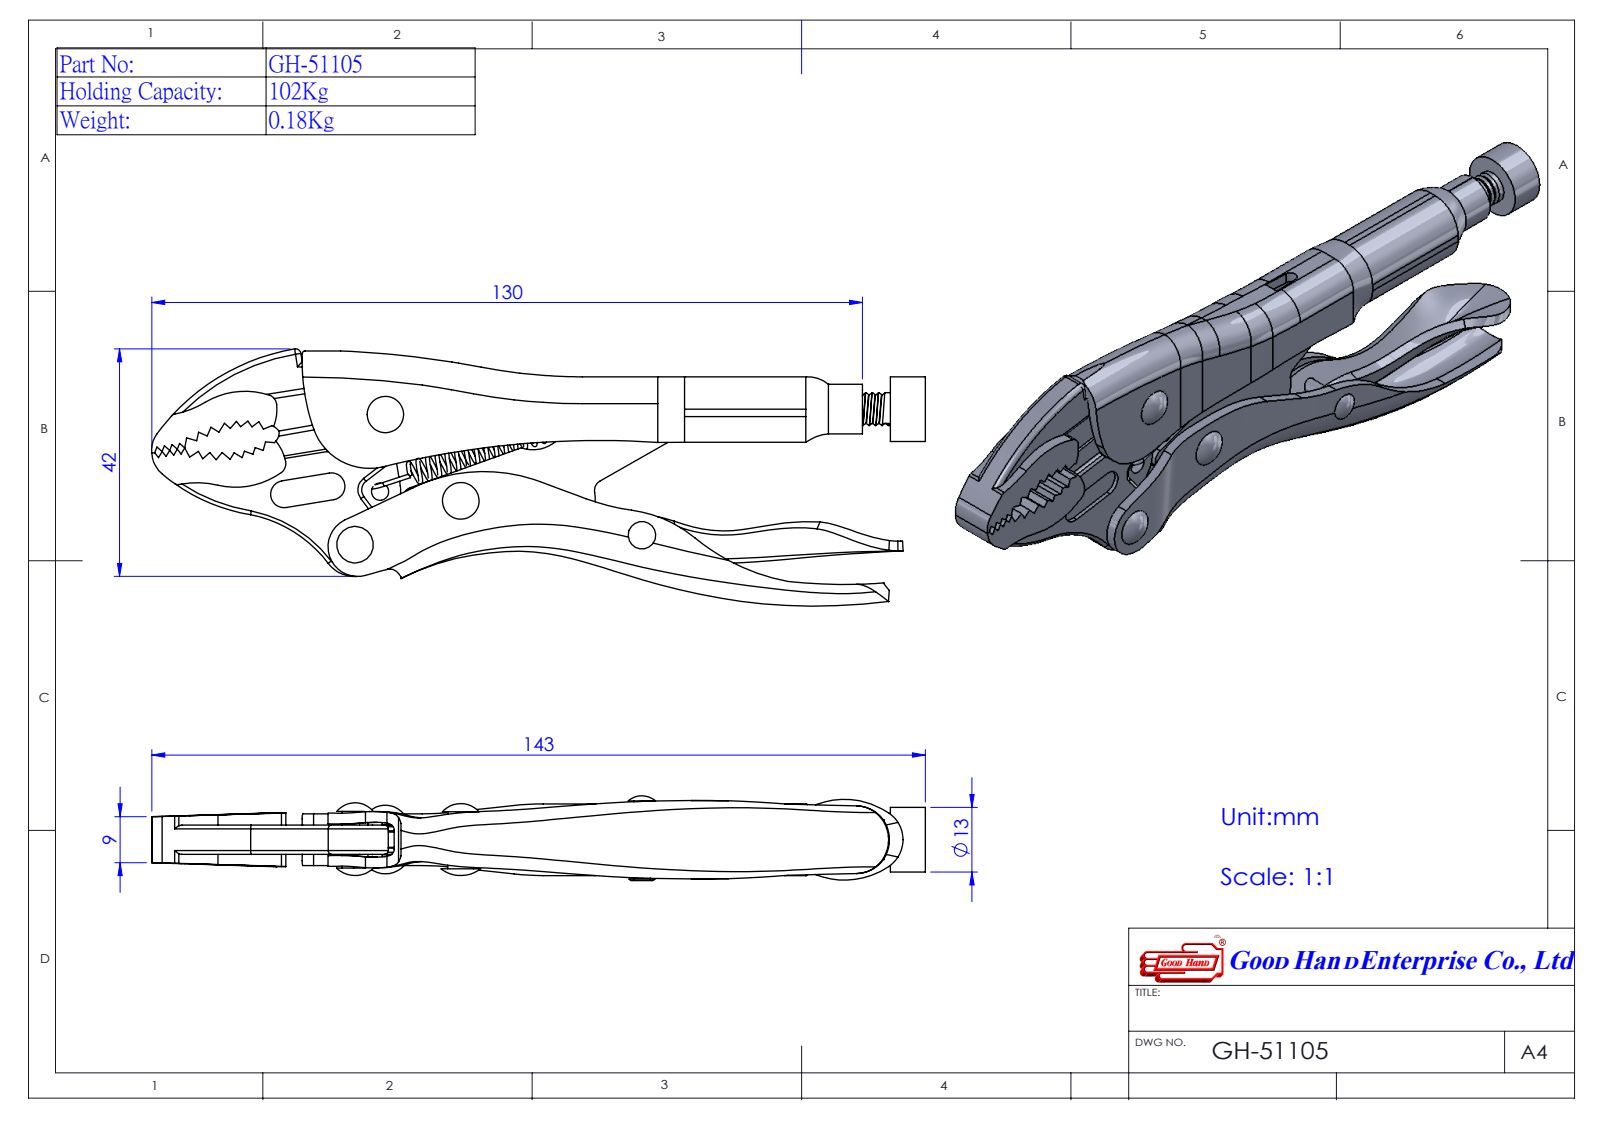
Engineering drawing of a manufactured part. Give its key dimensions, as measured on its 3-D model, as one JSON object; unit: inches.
{"part_name": "Group1^GH-51105(簡化); GH-51105(簡化)", "step_written_by": "SolidWorks 2016 (AUTOMOTIVE_DESIGN)", "units": "inches", "bodies": {"solids": 12, "faces": 572, "planar": 167, "cylindrical": 267, "other": 138}, "overall_size": [5.63, 1.856, 0.619], "volume_in3": 1.524, "surface_area_in2": 36.78, "round_holes": [[0.205, 1]], "round_bosses_or_shafts": [[0.189, 3], [0.03, 2], [0.472, 1], [0.362, 1], [0.24, 1], [0.209, 1], [0.169, 1], [0.116, 1]], "partial_cylinders_radius": [[0.039, 14], [0.02, 12], [0.028, 12], [0.079, 8], [0.118, 7], [0.197, 5], [0.236, 4], [1.969, 4]], "face_to_face_distances": [0.079, 0.037, 0.175, 0.12, 0.258, 0.073, 0.372, 0.083, 0.295, 0.138]}
